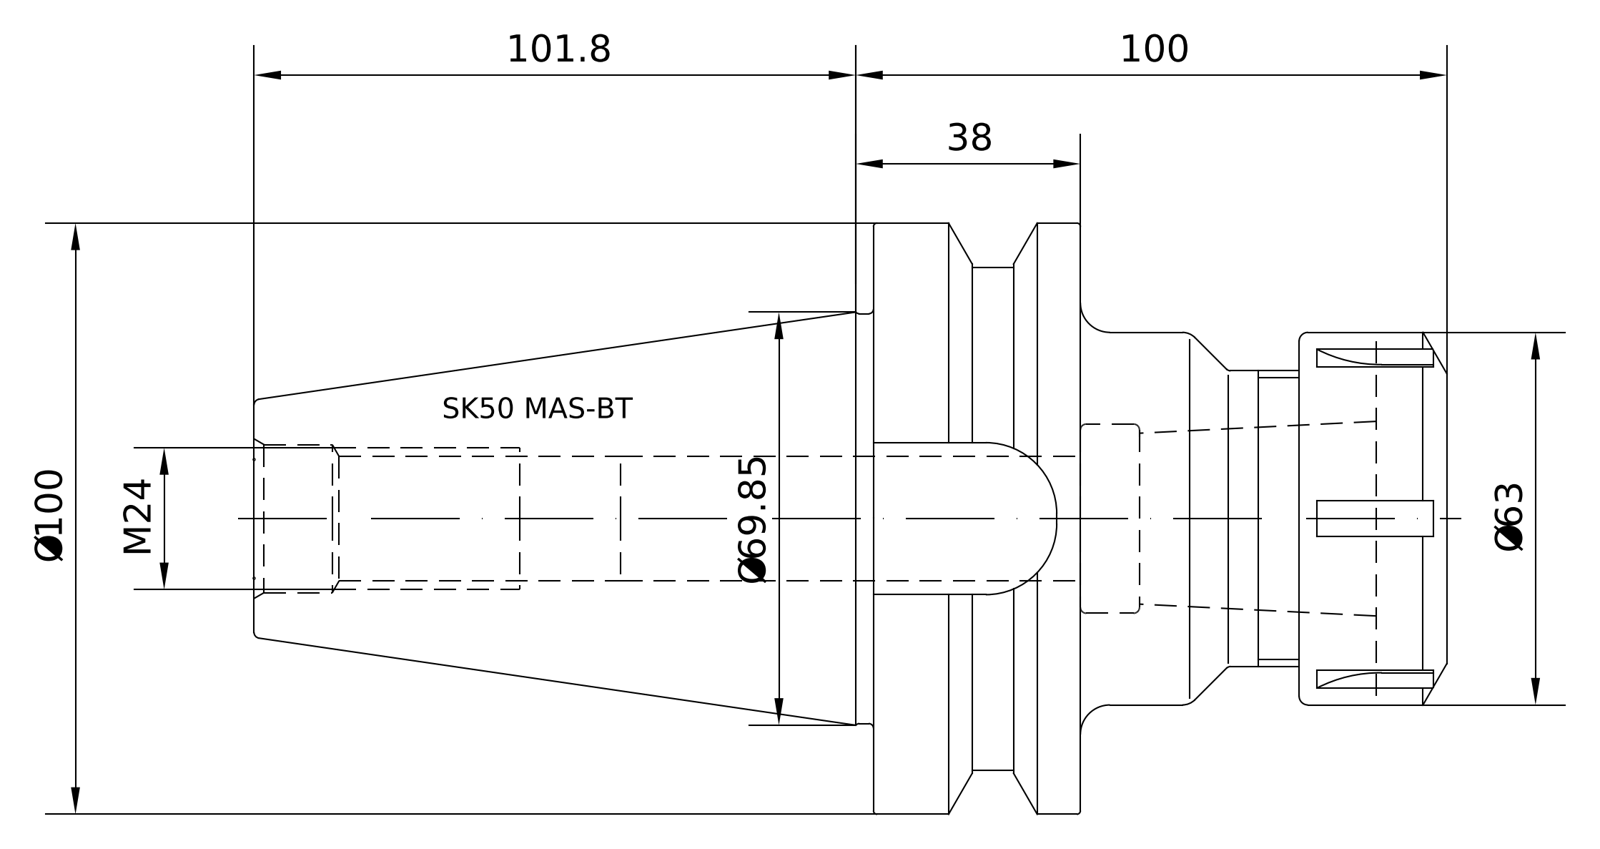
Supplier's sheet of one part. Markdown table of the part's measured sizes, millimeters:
| quantity | value |
| --- | --- |
| part name | 50-521-40; 83-912-40; 50-521-40_ASM |
| STEP written by | PRO/ENGINEER BY PARAMETRIC TECHNOLOGY CORPORATION, 2010430 (CONFIG_CONTROL_DESIGN) |
| units | millimeters |
| bodies | 2 solids, 148 faces (54 planar, 32 cylindrical, 62 other) |
| overall size | 201.8 × 99.97 × 99.97 |
| volume | 626 257 mm³ |
| surface area | 73 601 mm² |
| round holes (diameter × count) | 20.75 × 1, 25.02 × 1, 25.7 × 1, 30.5 × 1 |
| round bosses / shafts (diameter × count) | 99.97 × 1, 84.75 × 1, 69.15 × 1, 63 × 1, 50 × 1, 24.01 × 1 |
| partial cylindrical surfaces (radius × count) | 2.7 × 6, 12.9 × 1 |
| main face-to-face distances | 36.5, 35, 71.5, 97, 62, 25.5, 70.4, 44.1, 9.1, 27.4 |
